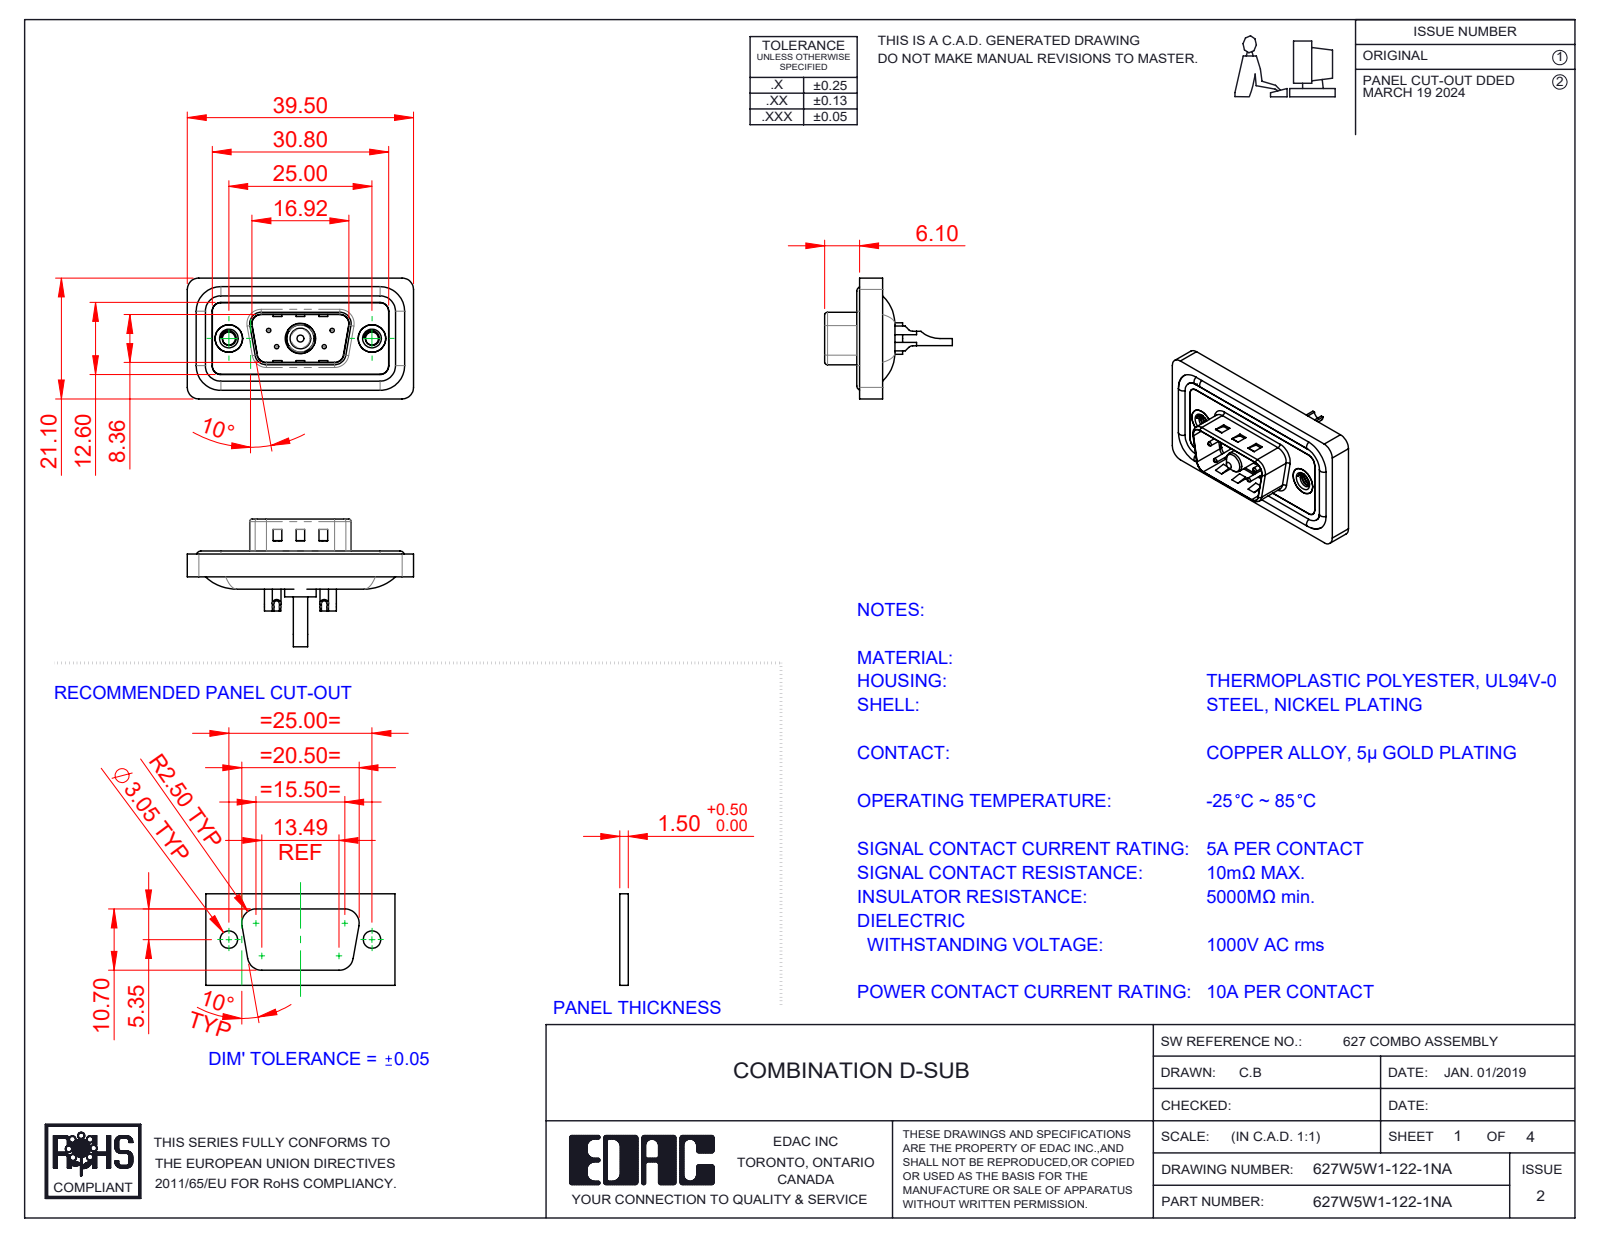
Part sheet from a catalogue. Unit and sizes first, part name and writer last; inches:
Units: inches
Overall size (bounding box): 1.555 × 0.878 × 0.831
Round holes (diameter × count): ⌀0.03 ×4, ⌀0.039 ×4, ⌀0.063 ×4, ⌀0.079 ×4, ⌀0.089 ×2, ⌀0.157 ×2, ⌀0.189 ×2, ⌀0.197 ×2, ⌀0.067 ×1, ⌀0.191 ×1, ⌀0.209 ×1
Round bosses / shafts (diameter × count): ⌀0.063 ×4, ⌀0.059 ×4, ⌀0.193 ×2, ⌀0.217 ×1, ⌀0.205 ×1, ⌀0.187 ×1, ⌀0.148 ×1, ⌀0.142 ×1
Partial cylindrical surfaces — rounded edges, fillets, slot ends (radius × count): R0.059 ×22, R0.079 ×18, R0.02 ×8, R0.063 ×8, R0.039 ×6, R0.01 ×4, R0.024 ×4, R0.026 ×4
Main face-to-face distances: 0.016, 0.043, 0.114, 0.063, 0.059, 0.122, 0.02, 0.098, 0.157, 0.031
Hole centre spacings: 0.124, 0.225, 0.28, 0.492, 0.713, 0.173, 0.173, 0.327
Volume: 0.268 in³ · Surface area: 10.88 in²
Bodies: 13 solids, 601 faces (193 planar, 268 cylindrical, 140 other)
Part name (STEP PRODUCT): 627Combo Shell Rear_09 Contacts; 627Combo Contact Row 1_22; Power Pin_10A SC; 627Combo Housing_5W1 (+5 more)
STEP written by: SolidWorks 2023 (CONFIG_CONTROL_DESIGN)
